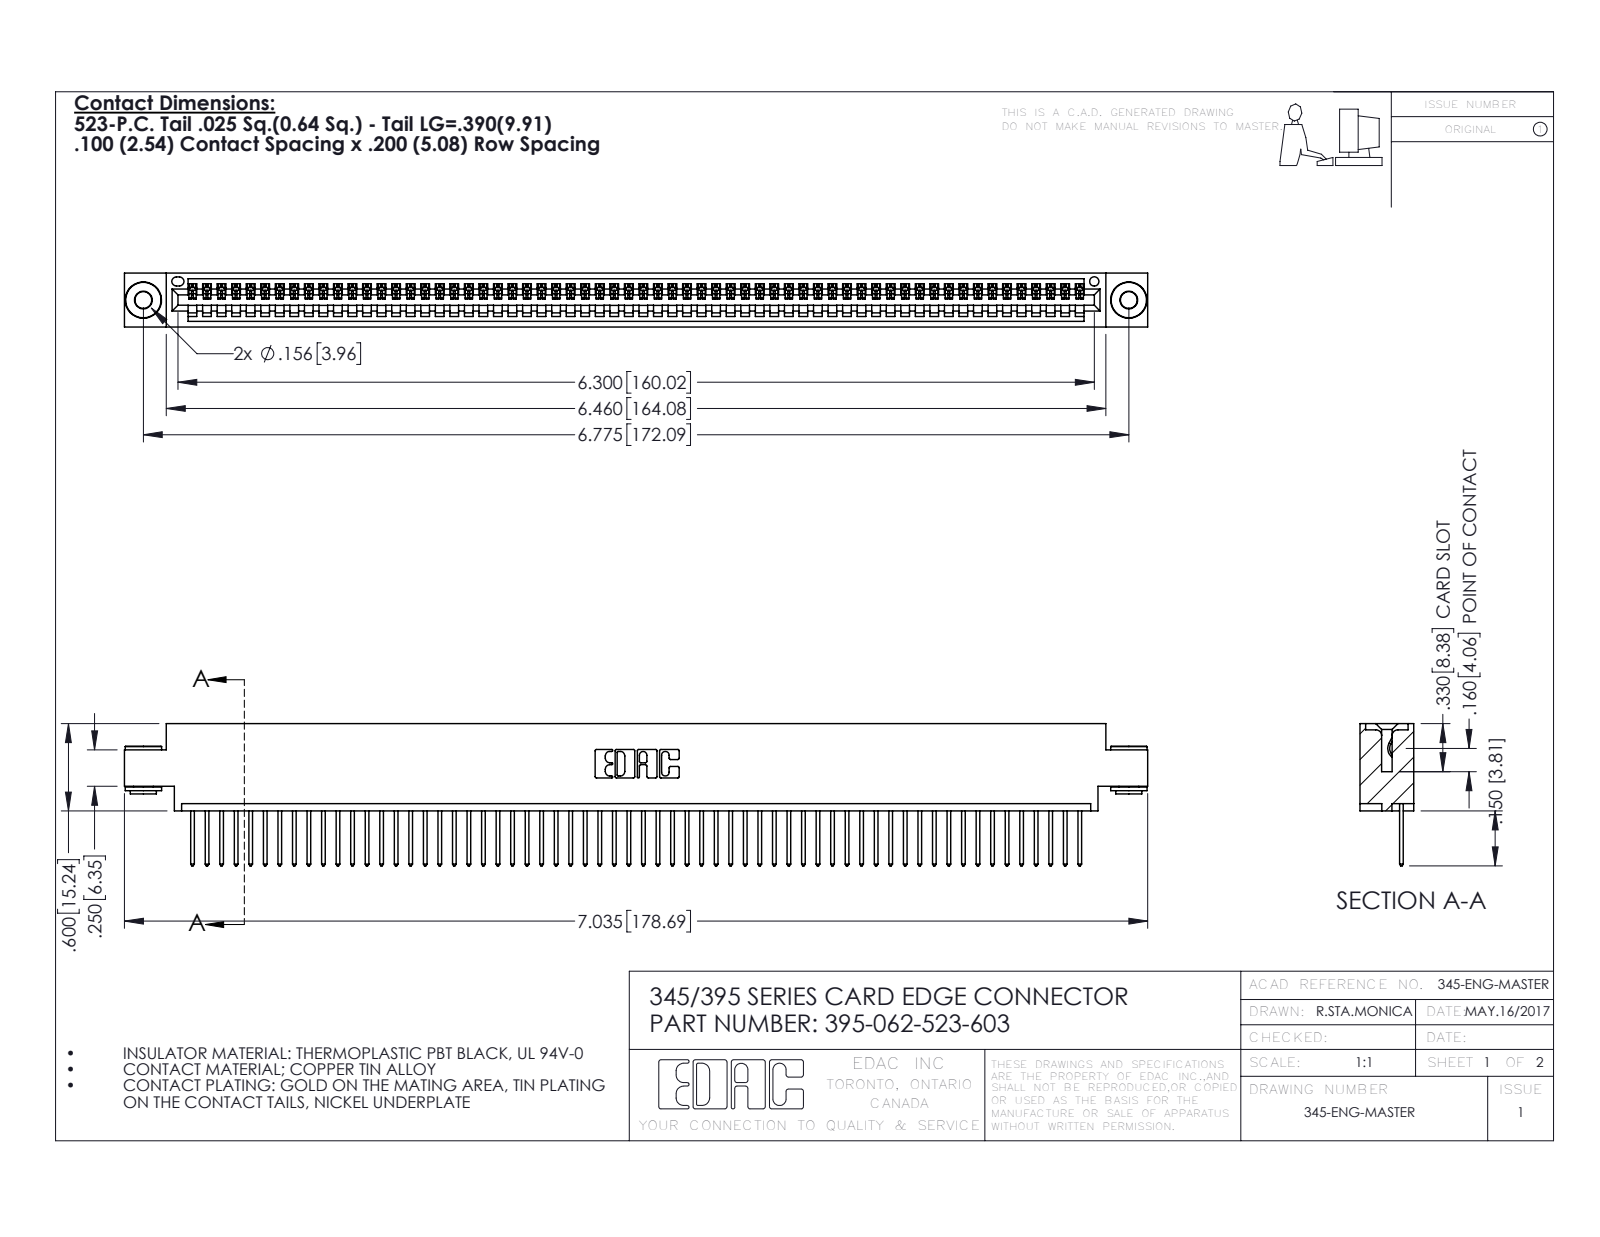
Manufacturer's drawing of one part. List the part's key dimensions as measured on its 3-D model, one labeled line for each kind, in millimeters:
Part name (STEP PRODUCT): 345-292-001_345-293-123; 345-250-002_345-250-002-102; 345 Part_0.170 Offset - 0.156 Dia-TH; 395-062-523-603
STEP written by: SolidWorks 2016 (CONFIG_CONTROL_DESIGN)
Units: millimetres
Bodies: 65 solids, 3764 faces (2574 planar, 1182 cylindrical, 8 other)
Overall size (bounding box): 178.7 × 24.8 × 9.4
Volume: 17 010 mm³ · Surface area: 23 300 mm²
Round holes (diameter × count): ⌀2.9 ×2, ⌀4 ×2, ⌀1.6 ×1
Round bosses / shafts (diameter × count): ⌀6.4 ×2, ⌀4.6 ×2, ⌀3.5 ×2
Partial cylindrical surfaces — rounded edges, fillets, slot ends (radius × count): R0.2 ×124, R0.3 ×124, R0.3 ×22, R0.2 ×6, R0.8 ×6, R0.7 ×3, R0.8 ×2, R1 ×2
Main face-to-face distances: 1.8, 7.6, 9.4, 2.5, 6.9, 0.6, 5.1, 5.7, 4.4, 3.8
Hole centre spacings: 6.9, 166.1, 172.1
